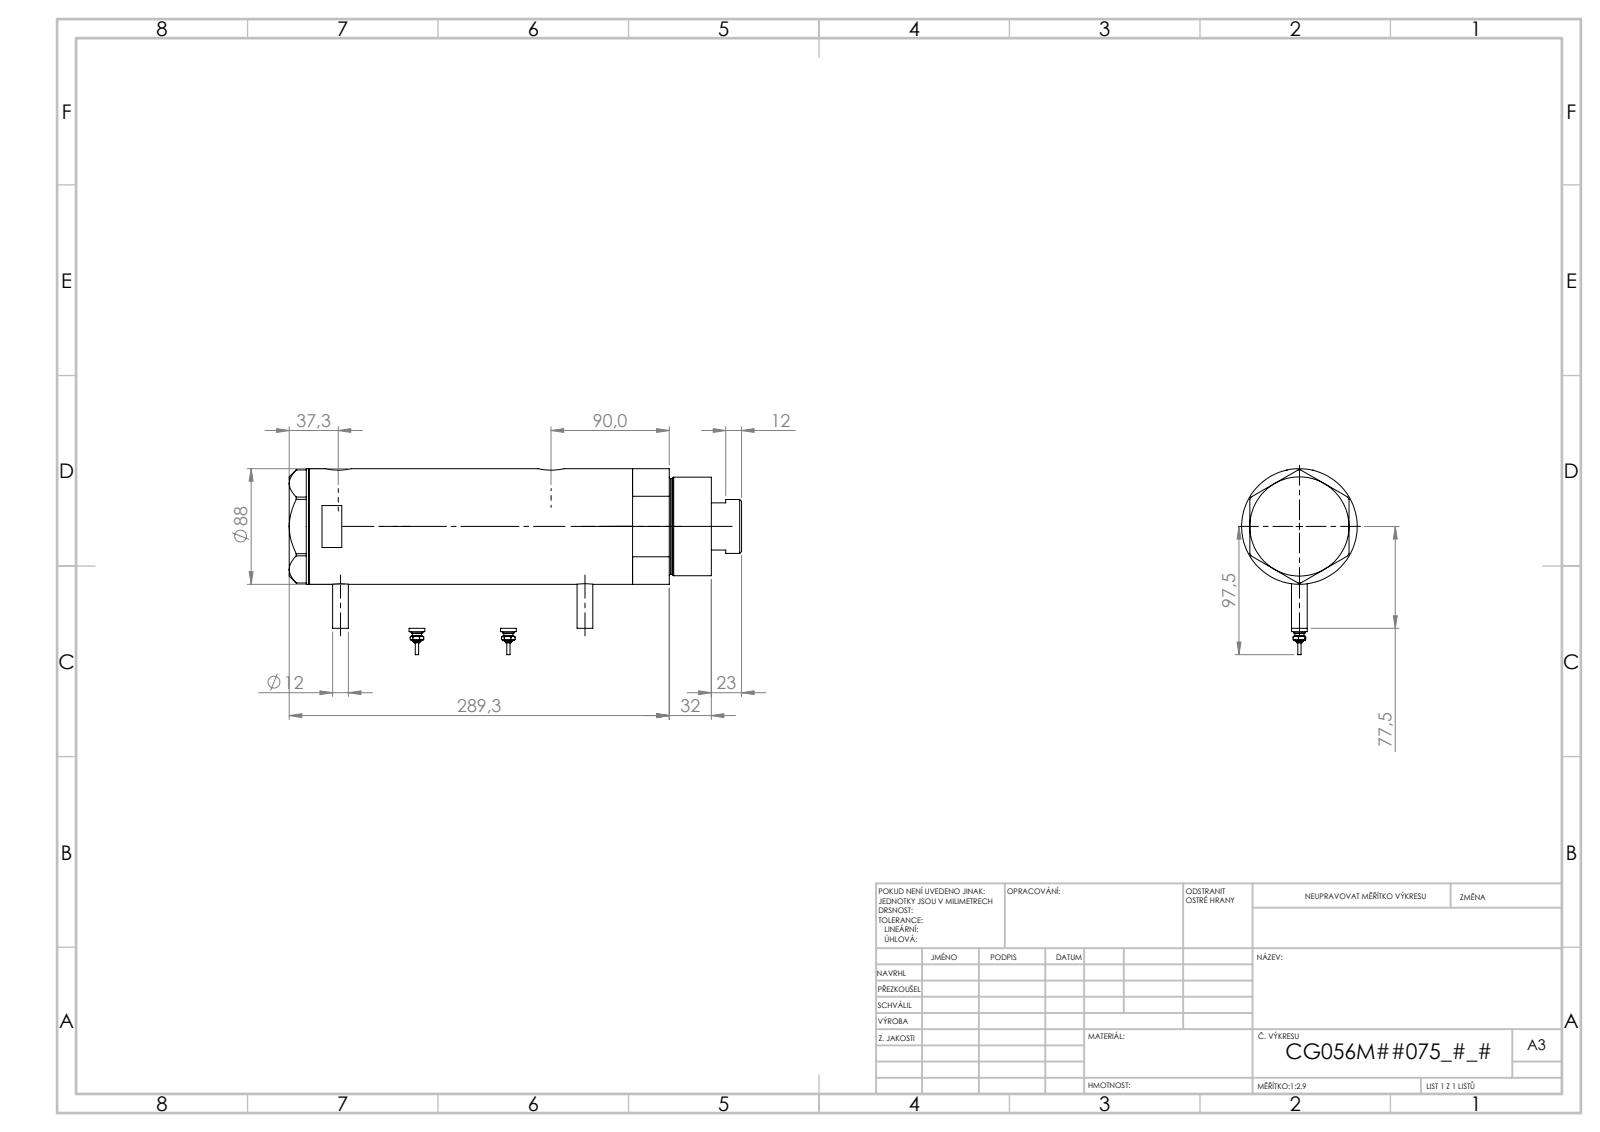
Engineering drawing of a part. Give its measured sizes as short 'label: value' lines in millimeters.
name: V270CG_BACK; V270CG_FRONT; V270CG_VC; V270CG_SWITCH (+1 more)
written by: SolidWorks 2019 (CONFIG_CONTROL_DESIGN)
unit: mm
bodies: 6 solids, 232 faces (81 planar, 77 cylindrical, 74 other)
size: 299.47 × 120.3 × 88
volume: 1 540 000 mm³; area: 226 032 mm²
holes: 2× ⌀5, 2× ⌀12.5, 2× ⌀13.16, 2× ⌀20, 1× ⌀14.5, 1× ⌀42, 1× ⌀43.5, 1× ⌀56, 1× ⌀60, 1× ⌀80
bosses: 2× ⌀12, 2× ⌀9, 2× ⌀7, 2× ⌀4.34, 2× ⌀2.4, 1× ⌀88, 1× ⌀75, 1× ⌀73
face distances: 149.4, 26, 123.4, 15, 41, 164.4, 261.47, 276.47, 235.47, 112.07
hole spacings: 1.7, 25.8, 125.3, 127, 151.1, 152.8
